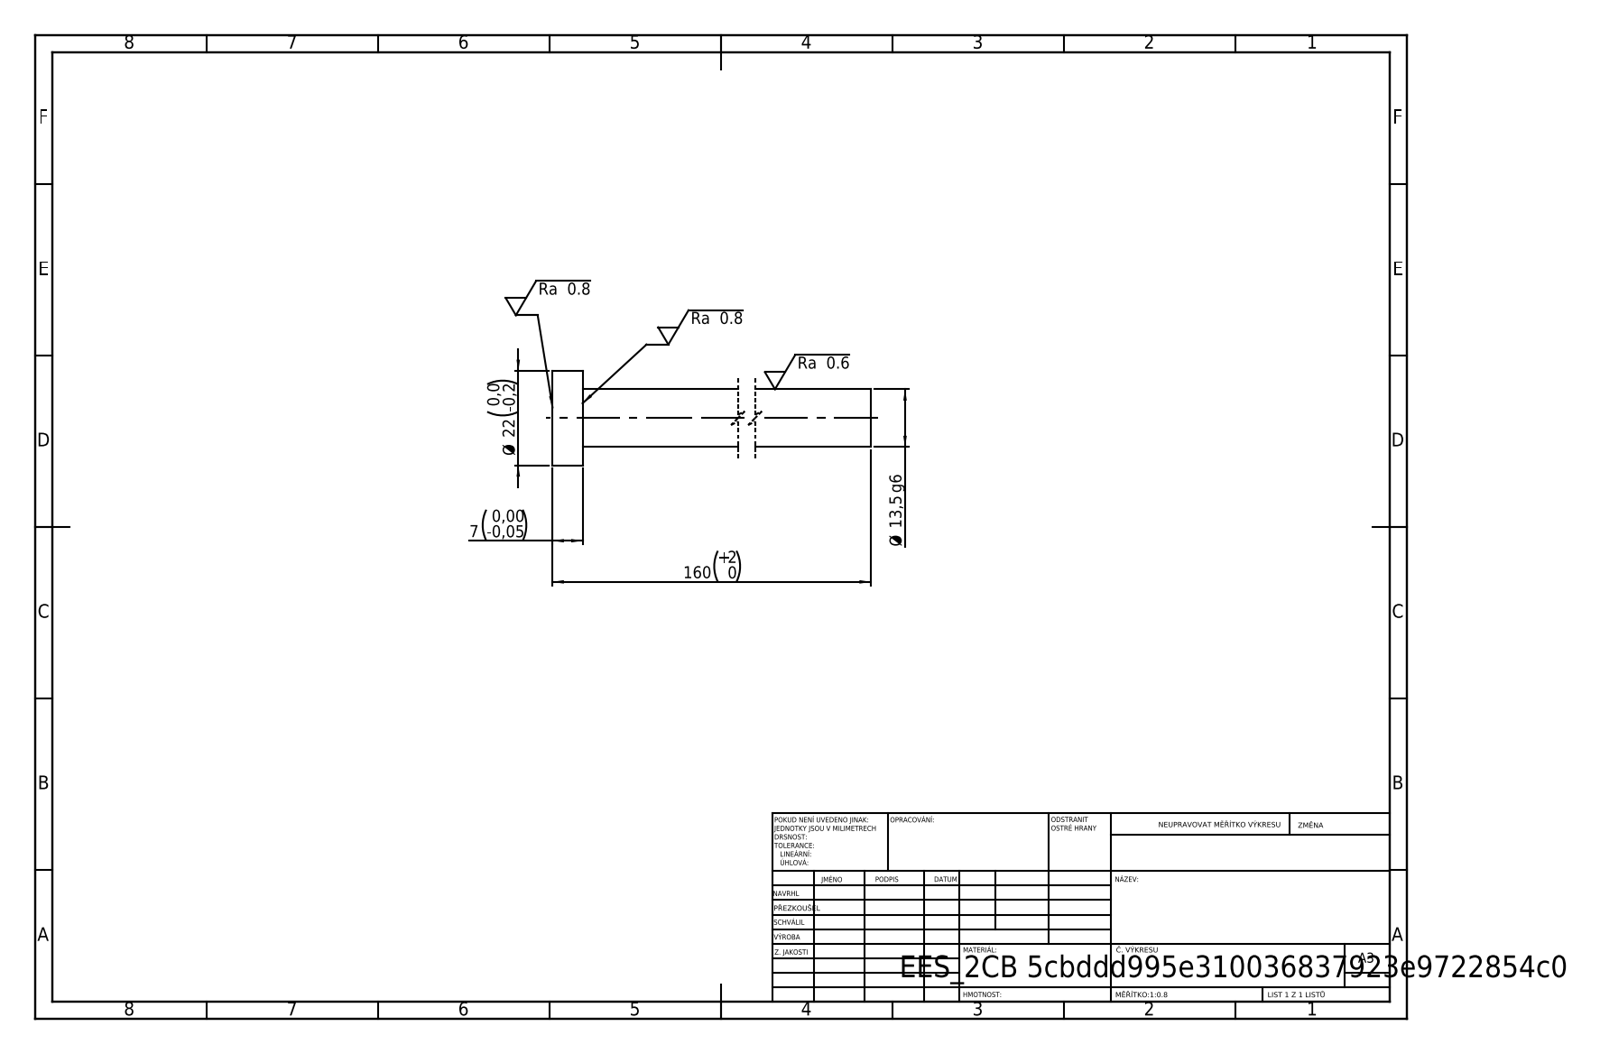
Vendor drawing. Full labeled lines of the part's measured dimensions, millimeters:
STEP written by: SolidWorks 2019 (CONFIG_CONTROL_DESIGN)
Units: millimetres
Bodies: 1 solid, 7 faces (3 planar, 4 cylindrical, 0 other)
Overall size (bounding box): 160 × 22 × 22
Volume: 24 561 mm³ · Surface area: 7 733 mm²
Round bosses / shafts (diameter × count): ⌀22 ×1, ⌀13.5 ×1
Main face-to-face distances: 7, 160, 153
